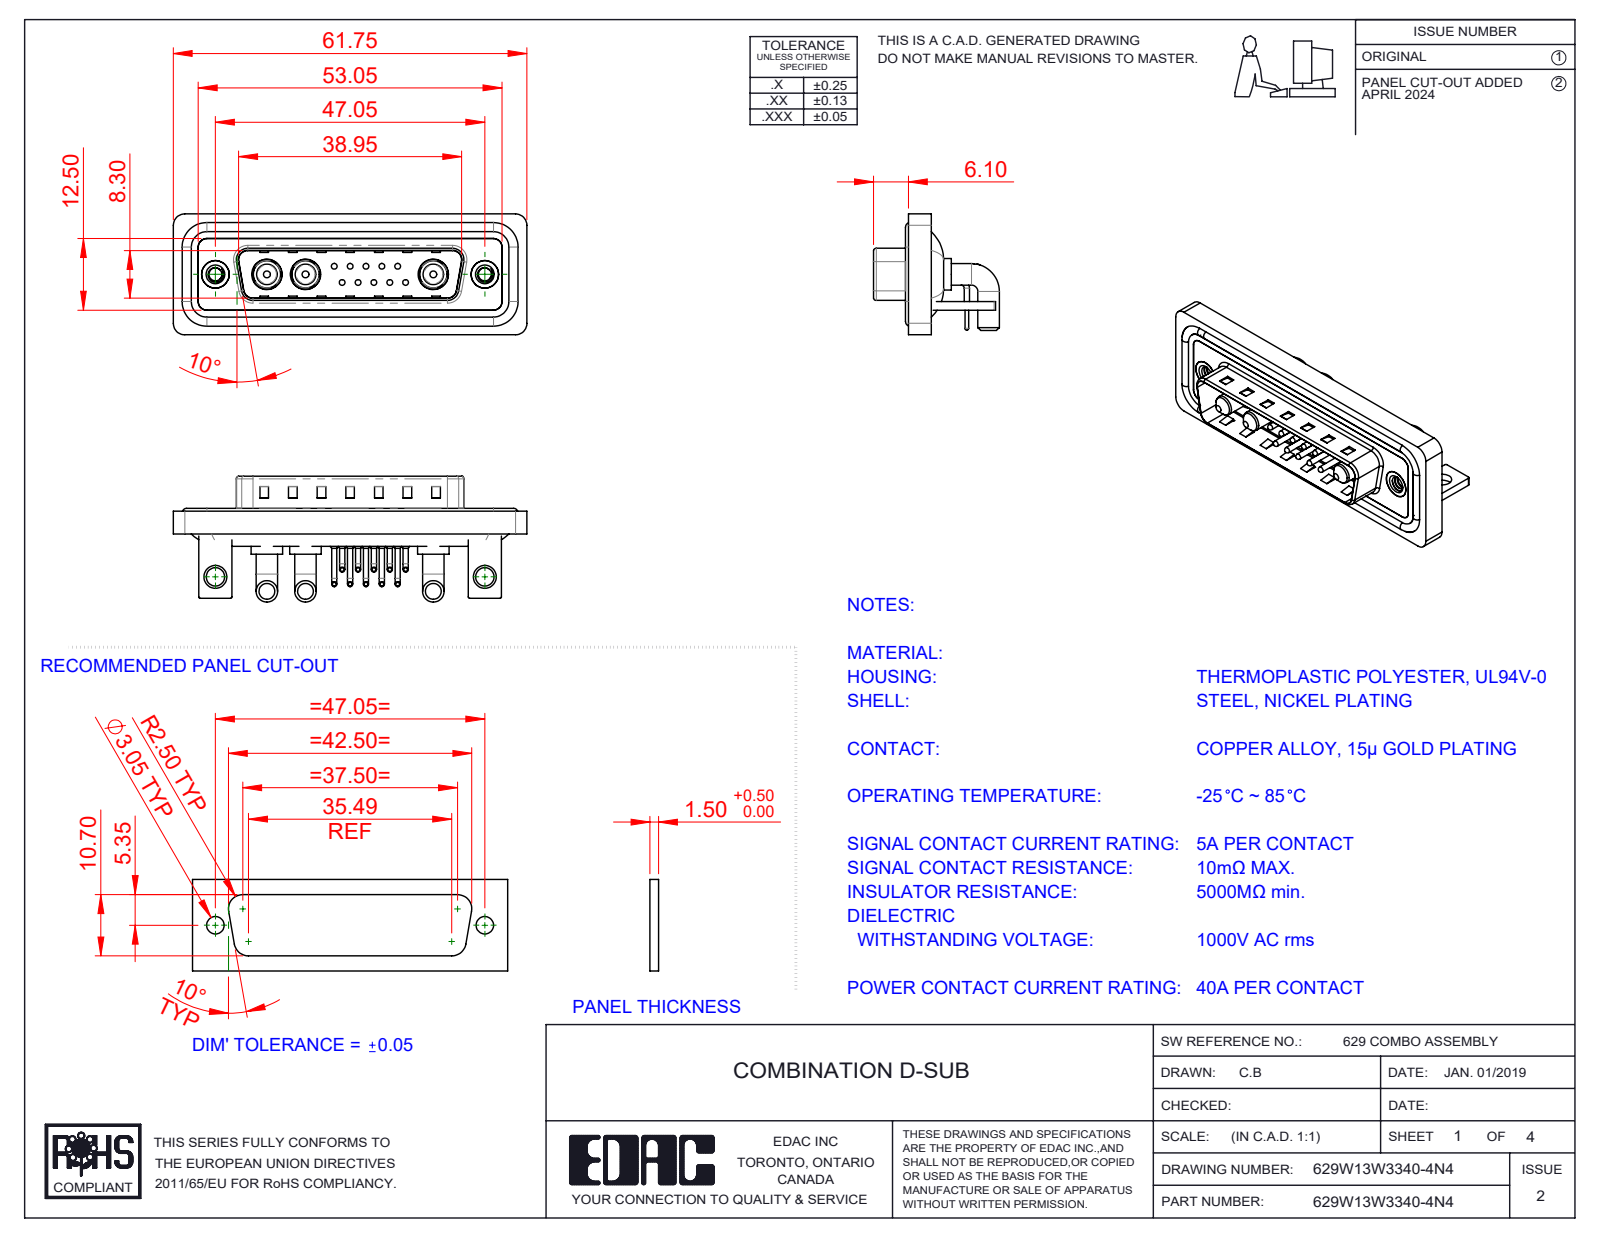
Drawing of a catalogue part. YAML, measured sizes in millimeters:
part_name: "629Combo Contact Row 2; 629W13W3340-4N4; 629Combo Shell Front_25 Contacts; Power Pin_40A RA (+6 more)"
step_written_by: "SolidWorks 2023 (CONFIG_CONTROL_DESIGN)"
units: millimeters
bodies: {solids: 25, faces: 1752, planar: 899, cylindrical: 629, other: 224}
overall_size: [61.75, 21.98, 21.1]
volume: 8106
surface_area: 13215
round_holes:
  - {diameter: 0.75, count: 10}
  - {diameter: 1.6, count: 10}
  - {diameter: 2, count: 10}
  - {diameter: 4.85, count: 3}
  - {diameter: 5.3, count: 3}
  - {diameter: 2.26, count: 2}
  - {diameter: 3.2, count: 2}
  - {diameter: 4, count: 2}
  - {diameter: 4.8, count: 2}
  - {diameter: 5, count: 2}
round_bosses_or_shafts:
  - {diameter: 0.9, count: 20}
  - {diameter: 1.5, count: 10}
  - {diameter: 1, count: 10}
  - {diameter: 0.65, count: 10}
  - {diameter: 3.75, count: 6}
  - {diameter: 1.6, count: 4}
  - {diameter: 5.5, count: 3}
  - {diameter: 5.2, count: 3}
partial_cylinders:
  - {radius: 2, count: 19}
  - {radius: 1.5, count: 18}
  - {radius: 0.25, count: 16}
  - {radius: 1.01, count: 10}
  - {radius: 0.5, count: 9}
  - {radius: 1.6, count: 8}
  - {radius: 0.6, count: 4}
  - {radius: 0.65, count: 4}
face_to_face_distances: [0.4, 0.8, 1.5, 2.9, 2.1, 1.1, 4.1, 1.6, 3.7, 4.5]
hole_center_spacings: [3.16, 2.77, 5.04, 5.54, 7.49, 5.03, 8.31, 10.11]
